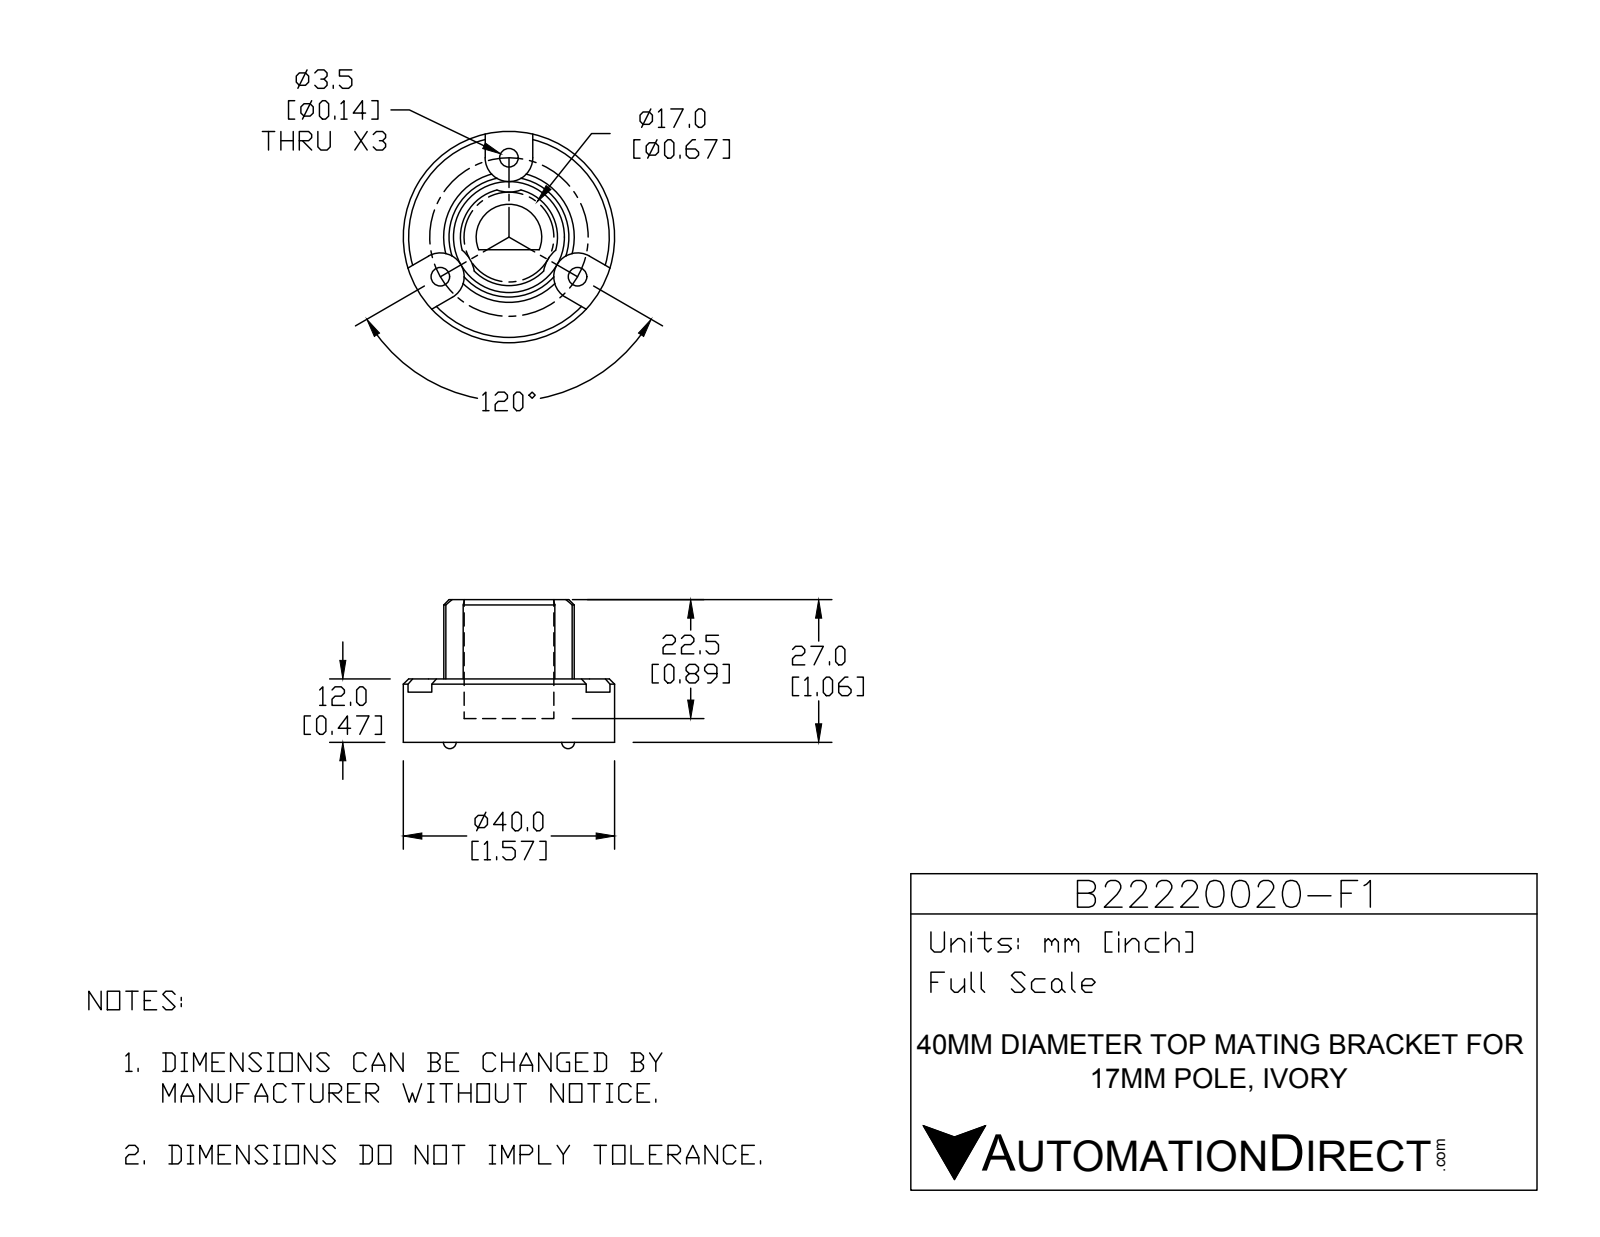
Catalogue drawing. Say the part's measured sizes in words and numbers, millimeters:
The part is named "B22220020-F1". Its 3-D file was written by "SolidWorks 2016 (AUTOMOTIVE_DESIGN)". It is 1 solid with 53 faces: 20 planar, 27 cylindrical and 6 other. Overall it measures 40 by 40 by 28.2 millimeters. Its volume is 14 741 cubic millimeters and its surface area 6 776 square millimeters. Round holes: 3 of diameter 3.5. Round bosses or shafts: 1 of diameter 40. Partial cylindrical surfaces (rounded edges, fillets, slot ends): 3 of radius 4.5, 3 of radius 6.5, 2 of radius 1.2, 1 of radius 6.2, 1 of radius 9.2, 1 of radius 12.35. The main face-to-face distances are 12, 9.5, 2.5, 4.5, 5, 7.5, 27, 22.5, 17.5, 15. The hole center spacings are 25.98.
